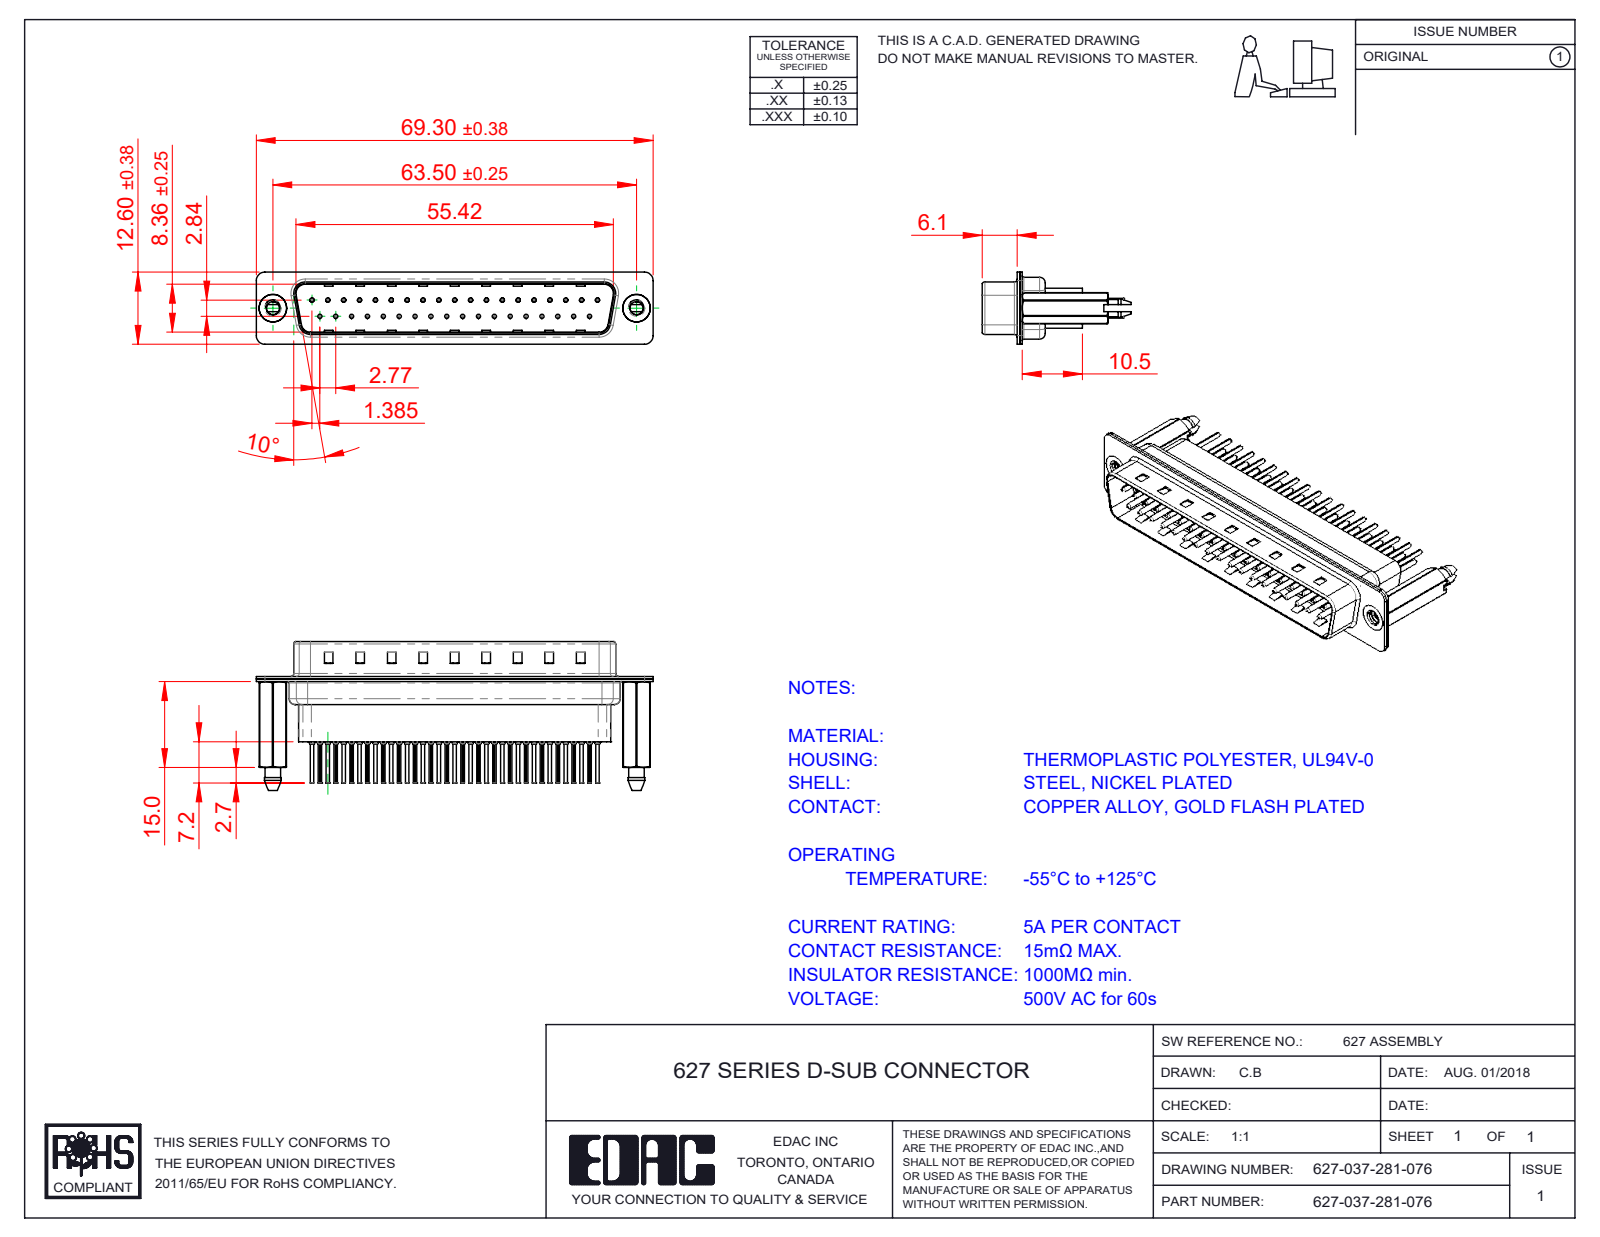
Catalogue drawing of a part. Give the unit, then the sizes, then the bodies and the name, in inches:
Units: inches
Overall size (bounding box): 2.728 × 1.02 × 0.496
Round holes (diameter × count): ⌀0.008 ×37, ⌀0.014 ×37, ⌀0.043 ×37, ⌀0.063 ×37, ⌀0.089 ×2, ⌀0.157 ×2, ⌀0.189 ×2
Round bosses / shafts (diameter × count): ⌀0.079 ×37, ⌀0.059 ×37, ⌀0.03 ×37, ⌀0.024 ×37, ⌀0.193 ×2
Partial cylindrical surfaces — rounded edges, fillets, slot ends (radius × count): R0.004 ×74, R0.059 ×18, R0.079 ×12, R0.063 ×10, R0.02 ×8, R0.01 ×4, R0.024 ×4, R0.026 ×4
Main face-to-face distances: 0.016, 0.032, 0.377, 0.027, 0.302, 0.018, 0.059, 0.043, 0.318, 0.345
Hole centre spacings: 0.124, 0.109, 0.218, 0.327, 0.198, 0.398, 0.436, 0.503
Volume: 0.349 in³ · Surface area: 22.85 in²
Bodies: 42 solids, 4146 faces (1123 planar, 1576 cylindrical, 1447 other)
Part name (STEP PRODUCT): 627 Housing_37 HP; 627 Shell Rear_37 Contacts; 627 Shell Front_37 Contacts; 627 4-40 Threaded Boardlock_HP81 (+3 more)
STEP written by: SolidWorks 2020 (CONFIG_CONTROL_DESIGN)
